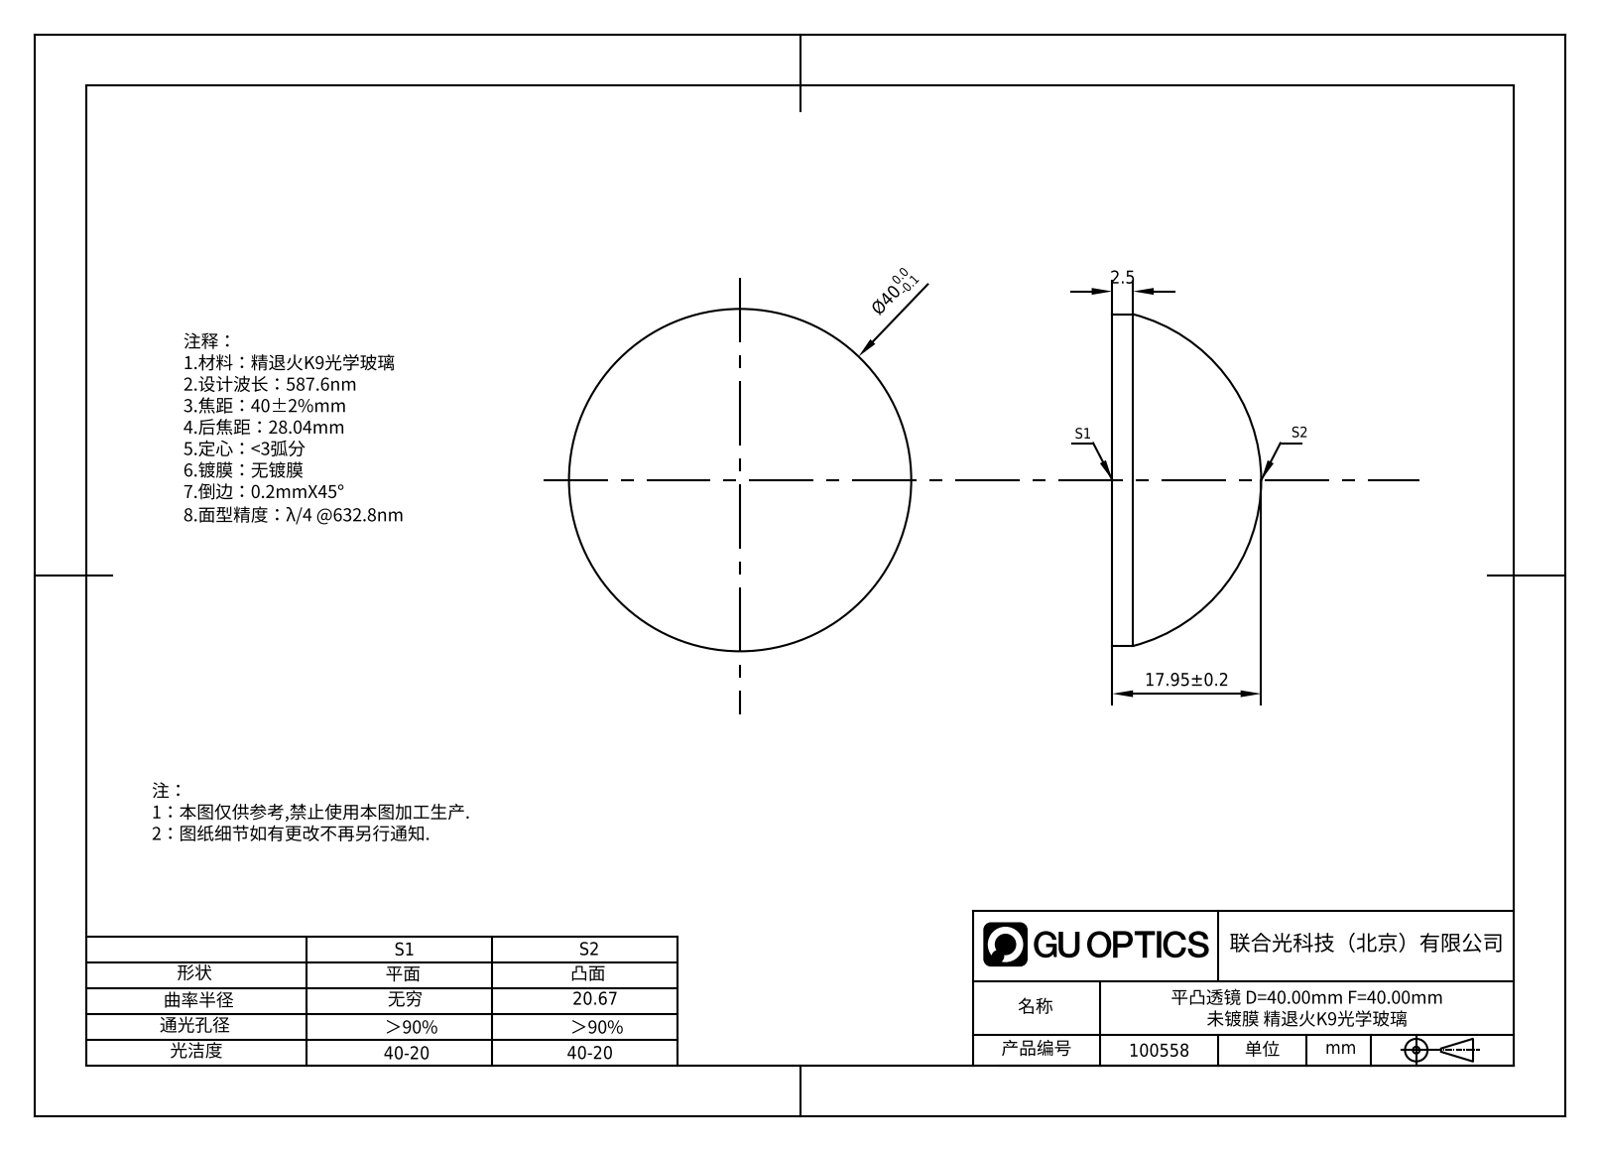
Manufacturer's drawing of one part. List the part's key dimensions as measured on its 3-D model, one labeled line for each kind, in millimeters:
Part name (STEP PRODUCT): 100558
STEP written by: SolidWorks 2020 (CONFIG_CONTROL_DESIGN)
Units: millimetres
Bodies: 1 solid, 5 faces (1 planar, 2 cylindrical, 2 other)
Overall size (bounding box): 40 × 40 × 17.95
Volume: 14 780 mm³ · Surface area: 3 577 mm²
Round bosses / shafts (diameter × count): ⌀40 ×1
